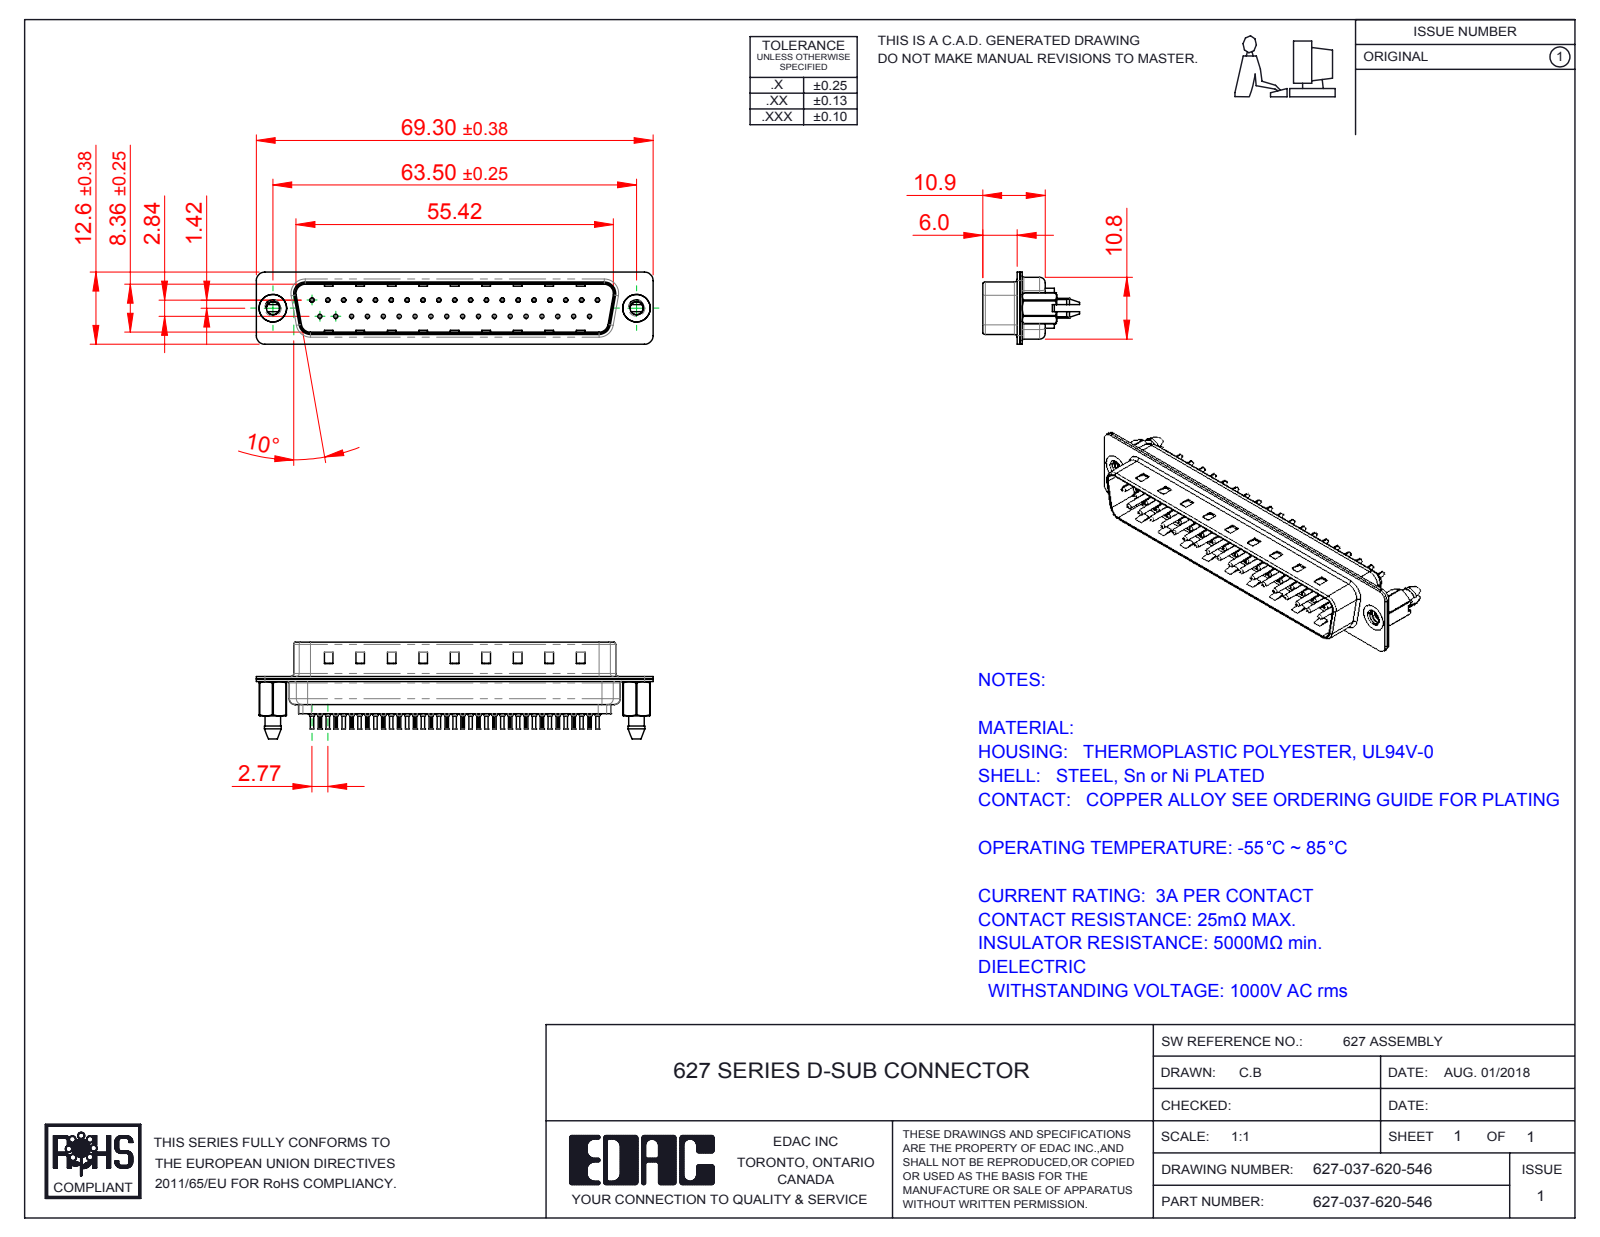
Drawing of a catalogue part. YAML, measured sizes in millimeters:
part_name: "627 Shell Front_37 Contacts; 627 Shell Rear_37 Contacts; 627 Contact Row 1_20L; 627 Housing_37 LP (+3 more)"
step_written_by: "SolidWorks 2016 (CONFIG_CONTROL_DESIGN)"
units: millimeters
bodies: {solids: 42, faces: 4112, planar: 1123, cylindrical: 1542, other: 1447}
overall_size: [69.3, 16.9, 12.6]
volume: 3797
surface_area: 10748
round_holes:
  - {diameter: 0.2, count: 37}
  - {diameter: 0.35, count: 37}
  - {diameter: 1.1, count: 37}
  - {diameter: 1.6, count: 37}
  - {diameter: 2.26, count: 2}
  - {diameter: 4, count: 2}
  - {diameter: 4.8, count: 2}
round_bosses_or_shafts:
  - {diameter: 2, count: 37}
  - {diameter: 1.5, count: 37}
  - {diameter: 0.75, count: 37}
  - {diameter: 0.6, count: 37}
  - {diameter: 4.9, count: 2}
partial_cylinders:
  - {radius: 0.1, count: 74}
  - {radius: 1.5, count: 18}
  - {radius: 2, count: 12}
  - {radius: 1.6, count: 10}
  - {radius: 0.5, count: 8}
  - {radius: 0.25, count: 4}
  - {radius: 0.6, count: 4}
  - {radius: 0.65, count: 4}
face_to_face_distances: [0.4, 0.82, 9.58, 0.45, 8.76, 1.5, 0.9, 1.4, 6.5, 6.05]
hole_center_spacings: [3.16, 2.77, 5.54, 8.31, 5.04, 10.1, 11.08, 12.78]
